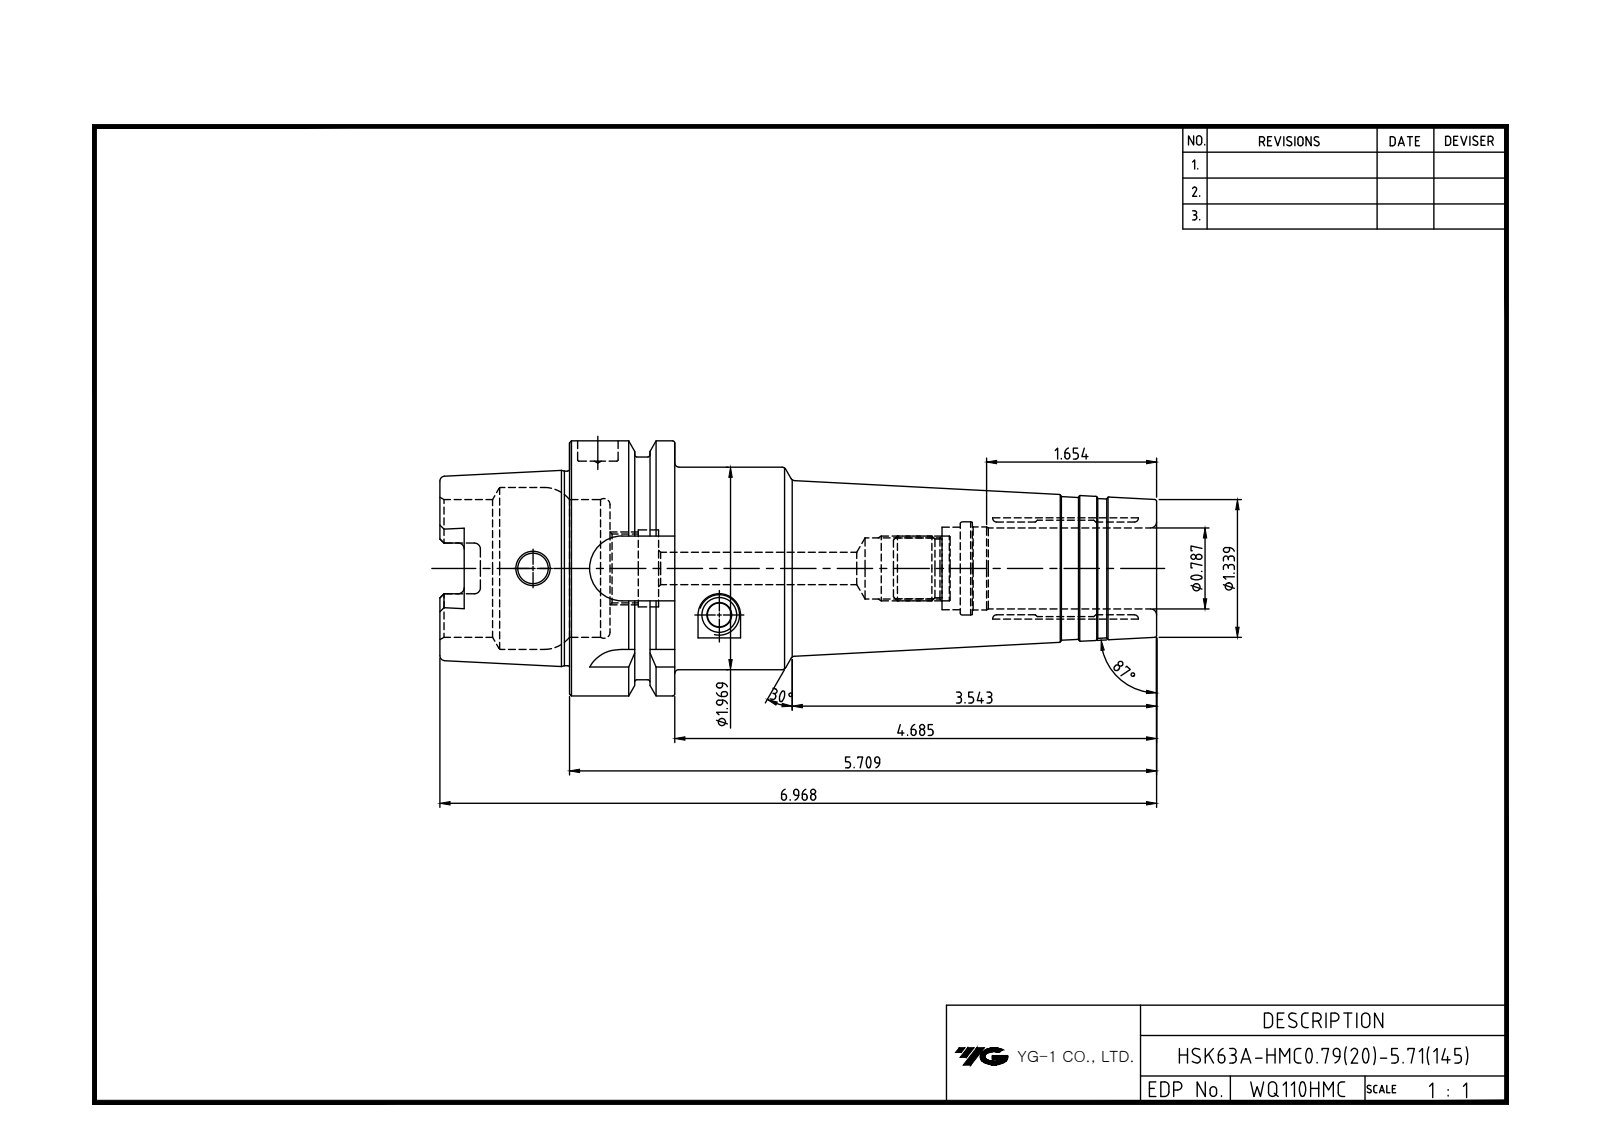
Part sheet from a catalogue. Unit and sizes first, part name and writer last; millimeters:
Units: millimetres
Overall size (bounding box): 177 × 63 × 63
Round holes (diameter × count): ⌀7.5 ×1, ⌀8 ×1, ⌀10 ×1, ⌀14.92 ×1, ⌀16.92 ×1, ⌀19 ×1, ⌀20 ×1, ⌀20.4 ×1, ⌀34 ×1, ⌀40 ×1
Round bosses / shafts (diameter × count): ⌀63 ×1, ⌀55 ×1, ⌀50 ×1, ⌀48.04 ×1
Partial cylindrical surfaces — rounded edges, fillets, slot ends (radius × count): R1.5 ×6, R2.88 ×4, R8 ×4
Main face-to-face distances: 26, 10, 16, 145, 135, 119, 53, 32, 42, 58
Volume: 221 449 mm³ · Surface area: 42 340 mm²
Bodies: 1 solid, 136 faces (41 planar, 34 cylindrical, 61 other)
Part name (STEP PRODUCT): HSK63A-HMC20-145
STEP written by: Autodesk Inventor 2020 (AUTOMOTIVE_DESIGN)
